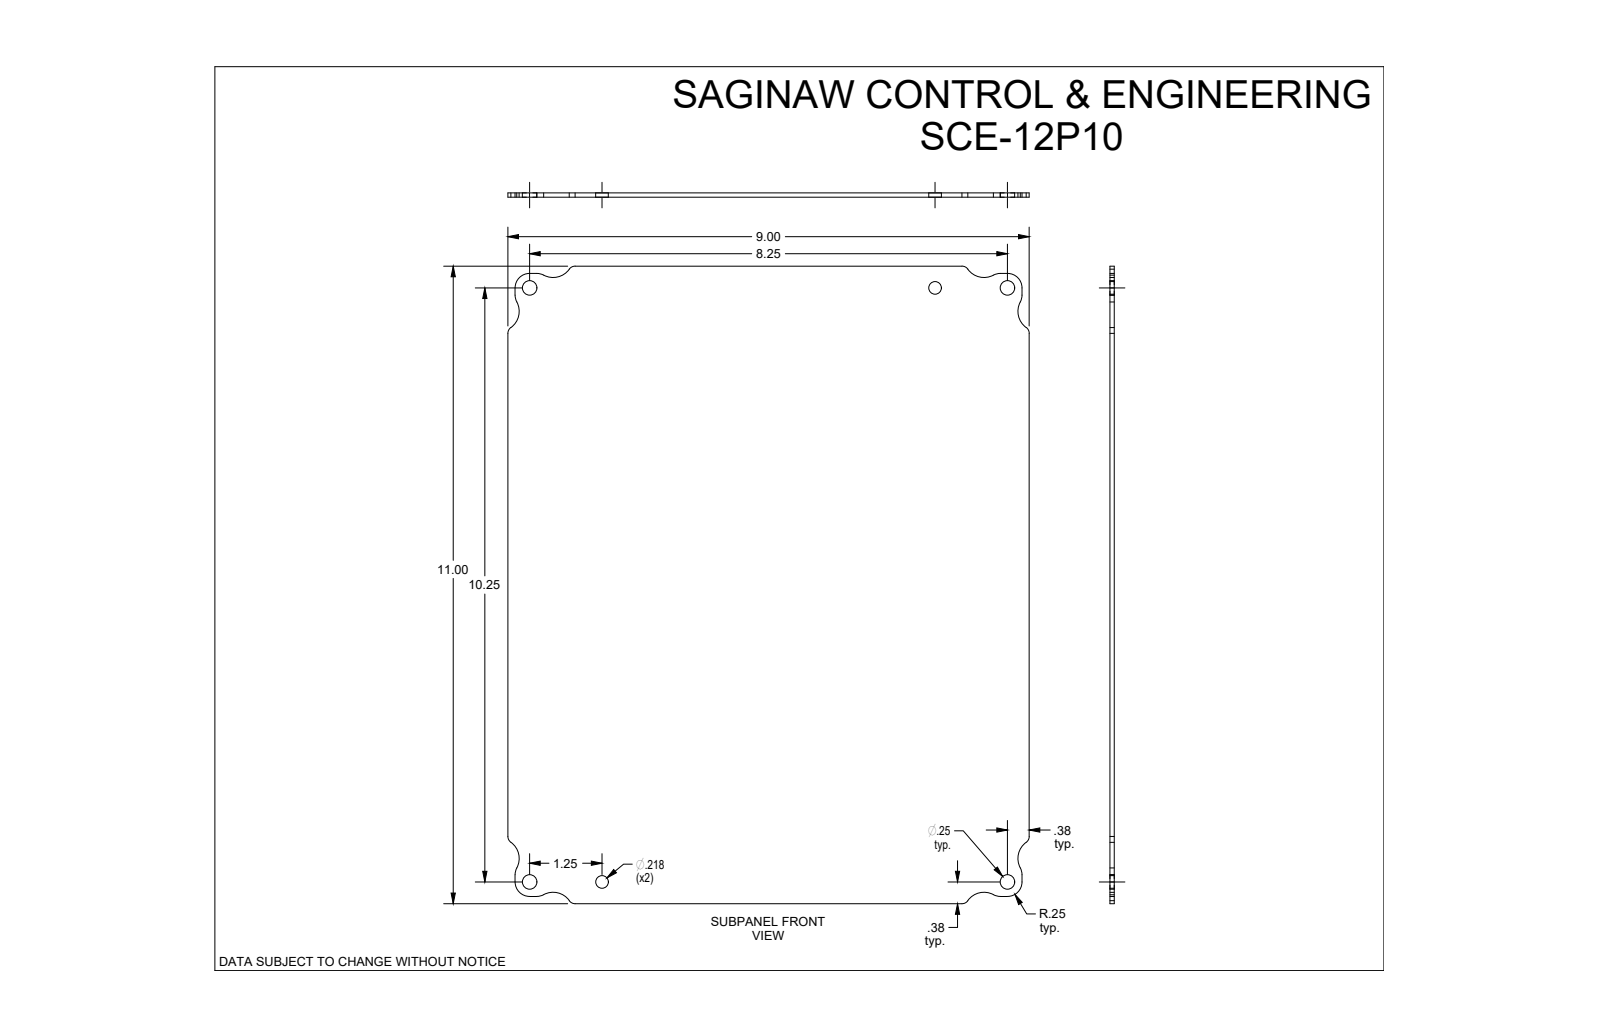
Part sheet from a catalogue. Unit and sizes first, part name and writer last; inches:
Units: inches
Overall size (bounding box): 11 × 9 × 0.075
Round holes (diameter × count): ⌀0.25 ×4, ⌀0.218 ×2
Partial cylindrical surfaces — rounded edges, fillets, slot ends (radius × count): R0.25 ×12, R0.125 ×8, R0.344 ×8
Main face-to-face distances: 0.075, 9, 11, 0.125, 10.875, 0.124, 8.876, 10.75, 8.752
Hole centre spacings: 1.25, 7, 8.25, 10.25, 10.326, 12.412, 13.157, 11.752
Volume: 7.314 in³ · Surface area: 198.3 in²
Bodies: 1 solid, 48 faces (14 planar, 34 cylindrical, 0 other)
Part name (STEP PRODUCT): SCE-12P10
STEP written by: SolidWorks 2019 (CONFIG_CONTROL_DESIGN)
